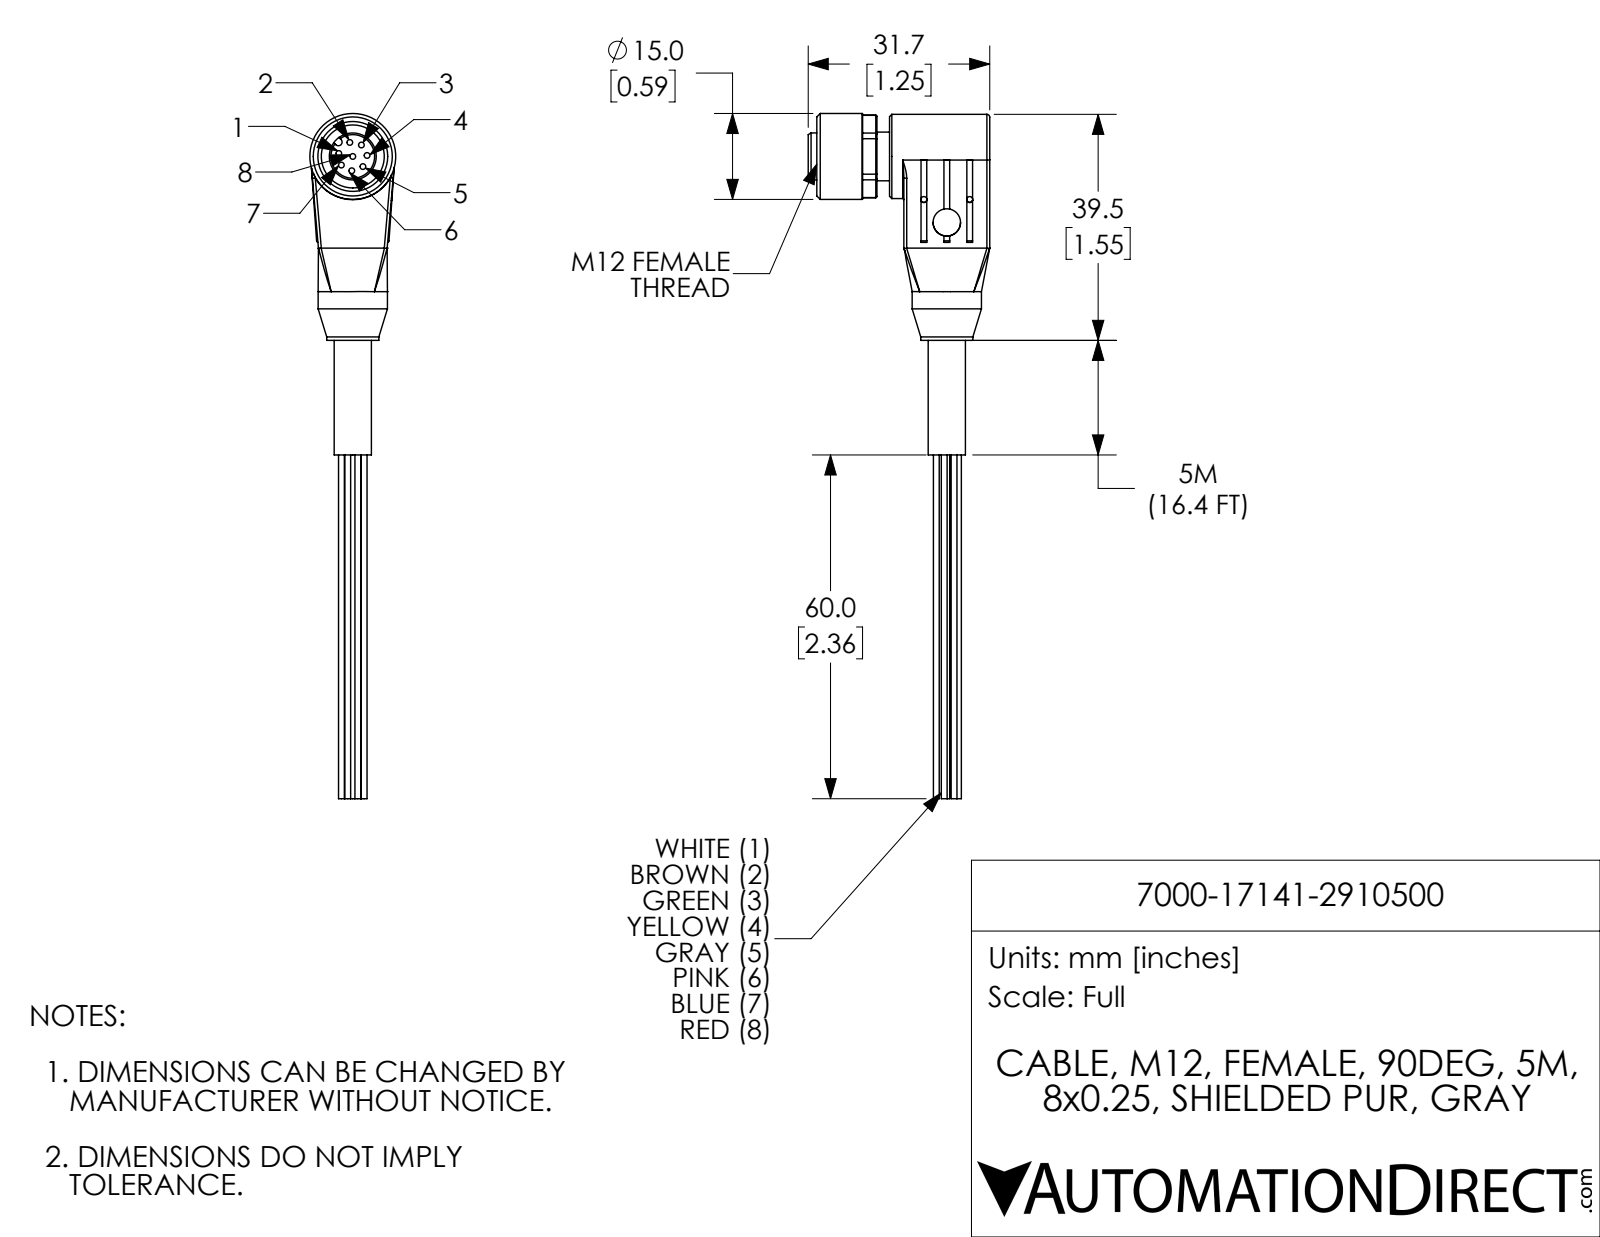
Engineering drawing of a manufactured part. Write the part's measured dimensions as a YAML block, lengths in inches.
part_name: "7000-17141-2910500"
step_written_by: "SolidWorks 2017 (AUTOMOTIVE_DESIGN)"
units: inches
bodies: {solids: 1, faces: 189, planar: 81, cylindrical: 75, other: 33}
overall_size: [4.709, 1.248, 0.591]
volume: 0.579
surface_area: 8.705
round_holes:
  - {diameter: 0.039, count: 8}
  - {diameter: 0.041, count: 4}
  - {diameter: 0.189, count: 1}
  - {diameter: 0.433, count: 1}
round_bosses_or_shafts:
  - {diameter: 0.04, count: 8}
  - {diameter: 0.591, count: 1}
  - {diameter: 0.579, count: 1}
  - {diameter: 0.476, count: 1}
  - {diameter: 0.358, count: 1}
  - {diameter: 0.335, count: 1}
  - {diameter: 0.323, count: 1}
  - {diameter: 0.256, count: 1}
partial_cylinders:
  - {radius: 0.02, count: 4}
  - {radius: 0.012, count: 2}
  - {radius: 0.026, count: 1}
  - {radius: 0.283, count: 1}
face_to_face_distances: [0.098, 0.591, 0.185, 0.689, 0.776, 0.087, 0.118, 0.303, 0.472, 0.657]
hole_center_spacings: [0.098, 0.081, 0.149, 0.195, 0.082, 0.166, 0.189, 0.189]
